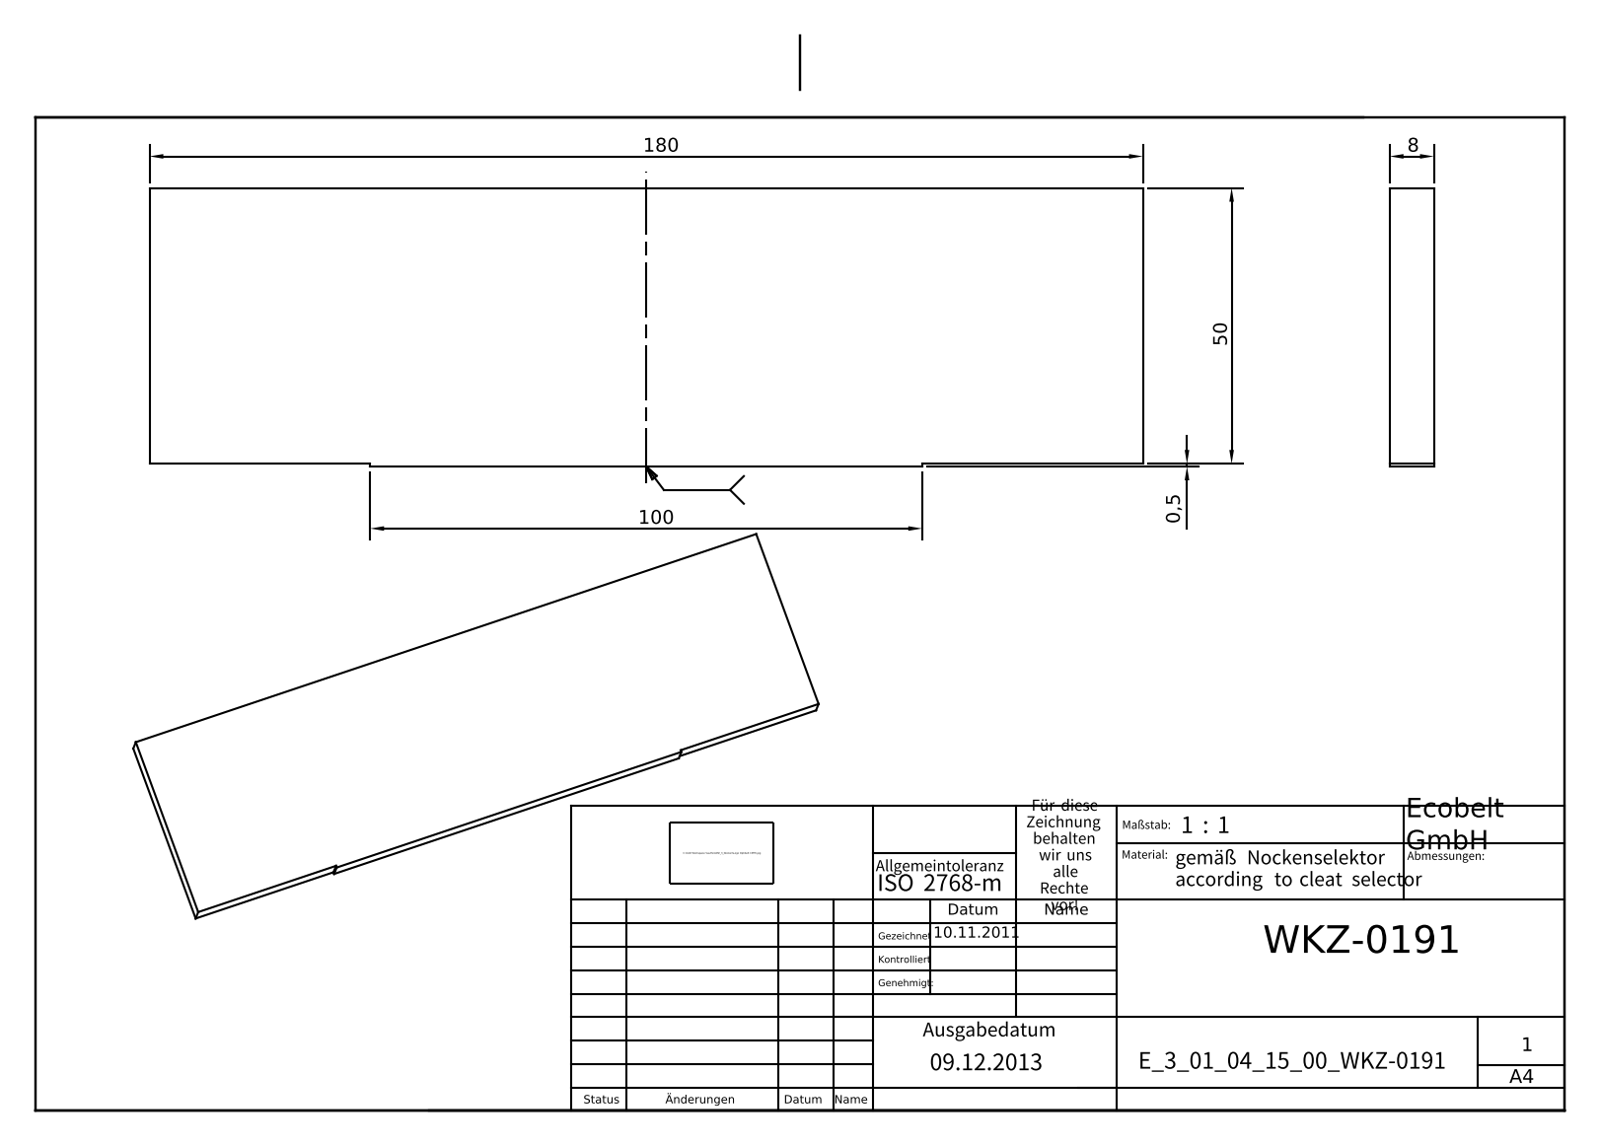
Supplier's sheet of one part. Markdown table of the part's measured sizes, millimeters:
| quantity | value |
| --- | --- |
| part name | E_3_01_04_15_00_WKZ-0191 |
| STEP written by | Autodesk Inventor 2025 (AUTOMOTIVE_DESIGN) |
| units | millimeters |
| bodies | 1 solid, 10 faces (10 planar, 0 cylindrical, 0 other) |
| overall size | 180 × 50.5 × 8 |
| volume | 72 400 mm³ |
| surface area | 21 788 mm² |
| main face-to-face distances | 8, 50.5, 0.5, 50, 180, 40, 140, 100 |
